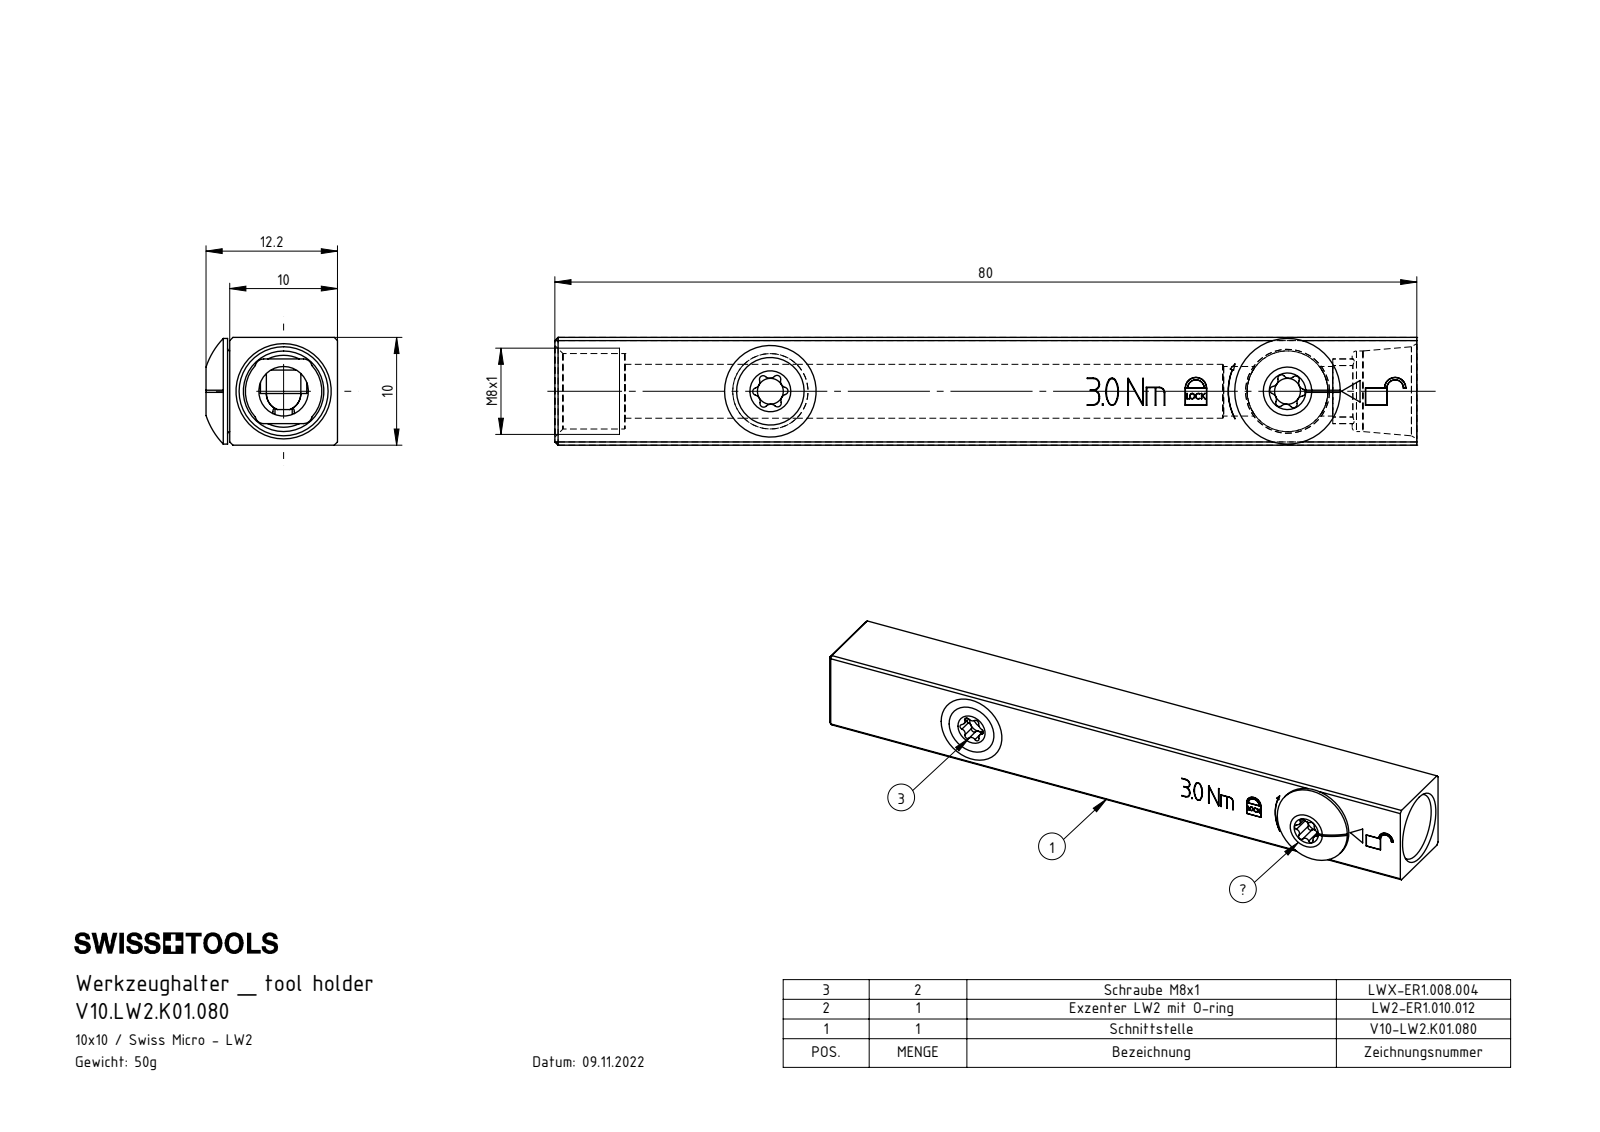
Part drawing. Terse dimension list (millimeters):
name: LWX-ER1.008.004_A; V10.LW2.K01.080; DIN 3771 - 5x1; V10-LW2.K01.080_C (+2 more)
written by: SolidWorks 2022 (AUTOMOTIVE_DESIGN)
unit: mm
bodies: 6 solids, 197 faces (91 planar, 71 cylindrical, 35 other)
size: 80 × 12.2 × 10
volume: 6 396 mm³; area: 5 726 mm²
holes: 3× ⌀2.4, 2× ⌀7, 1× ⌀1, 1× ⌀4.6, 1× ⌀5, 1× ⌀7.48
bosses: 2× ⌀8, 1× ⌀9.8, 1× ⌀7.5, 1× ⌀5.7
rounds: 12× R0.34, 12× R0.59, 6× R0.34, 6× R0.59, 4× R0.8, 2× R1.6, 1× R2.15, 1× R2.35
face distances: 10, 4, 13.72, 2, 1.1, 4.2, 6, 5.6, 0.4, 9.6
hole spacings: 48
